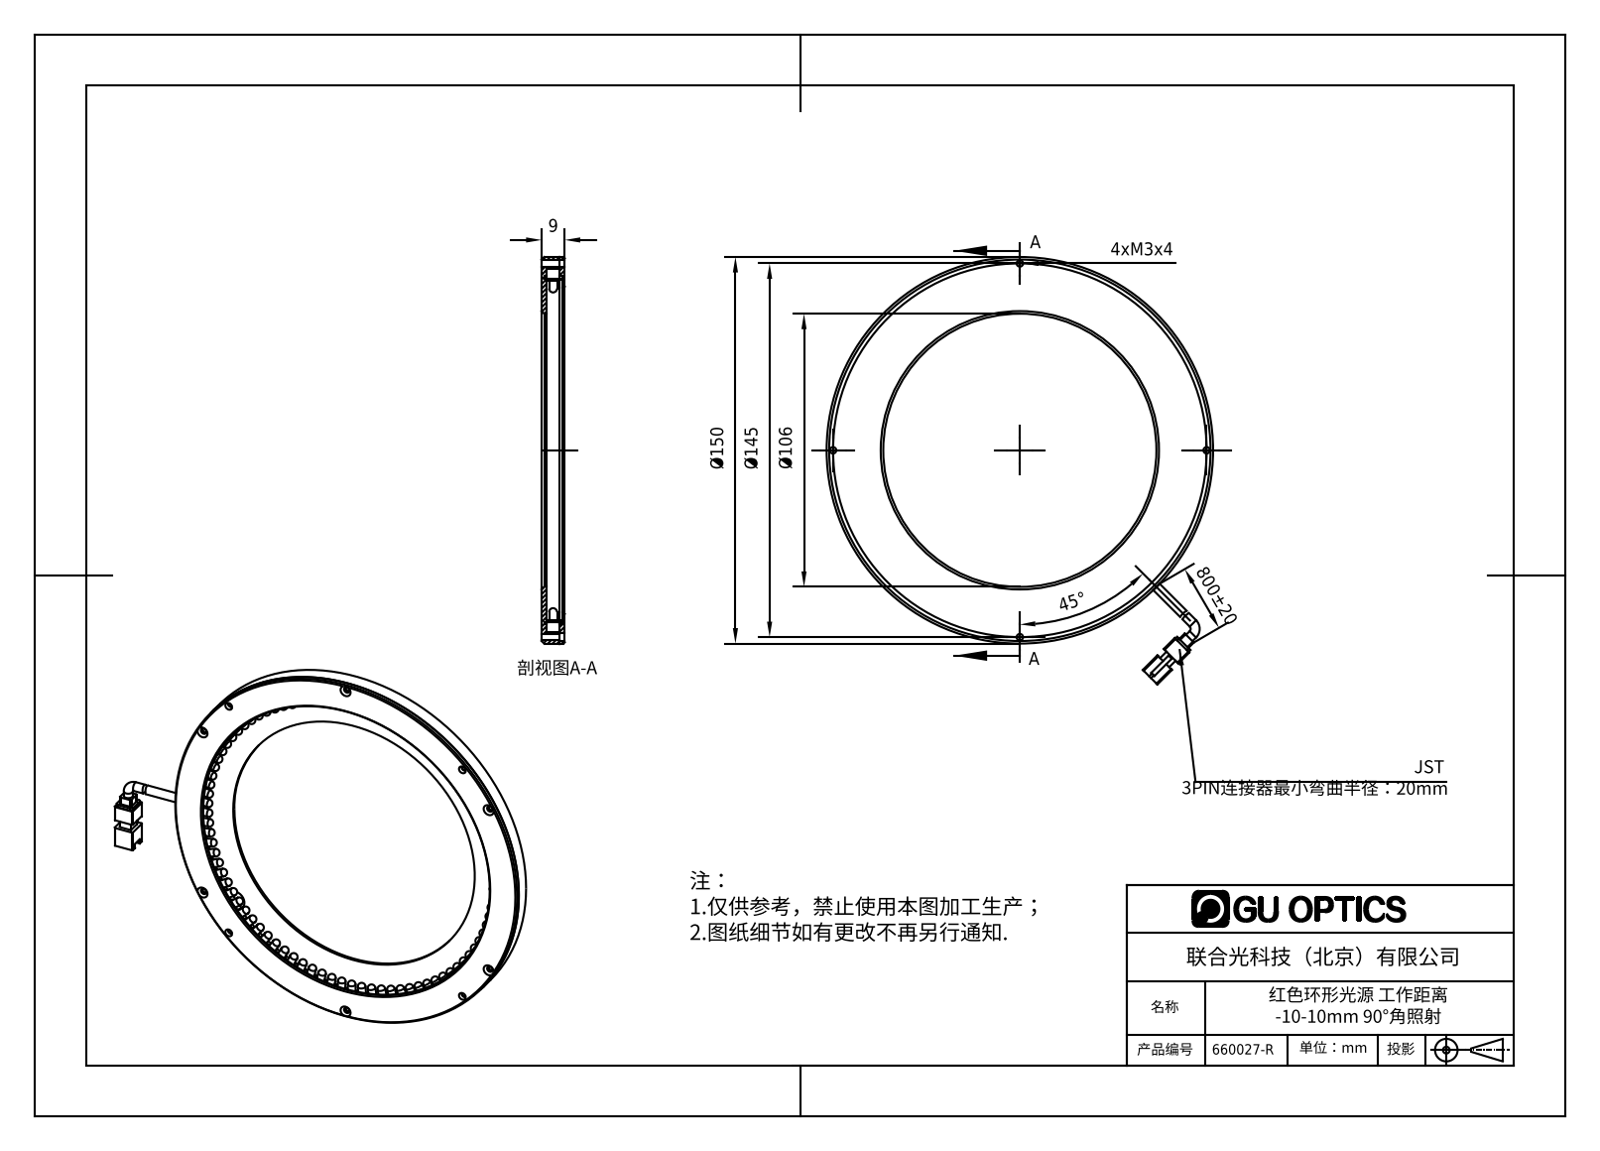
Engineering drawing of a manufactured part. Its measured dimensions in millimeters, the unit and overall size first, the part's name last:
Units: millimetres
Overall size (bounding box): 177 × 150 × 11
Round holes (diameter × count): ⌀1.6 ×6, ⌀2 ×6, ⌀2.4 ×6, ⌀2.5 ×4, ⌀3 ×4, ⌀8 ×2, ⌀3.5 ×1, ⌀106 ×1, ⌀126 ×1, ⌀132 ×1, ⌀135 ×1, ⌀141 ×1
Round bosses / shafts (diameter × count): ⌀4 ×90, ⌀3 ×90, ⌀3.5 ×2, ⌀150 ×1, ⌀134 ×1, ⌀133 ×1
Partial cylindrical surfaces — rounded edges, fillets, slot ends (radius × count): R0.5 ×8, R1 ×4, R2 ×2, R3.5 ×2
Main face-to-face distances: 2, 7, 5, 1, 9, 8, 6, 0.5, 1.5, 3.77
Hole centre spacings: 72.5, 72.49, 145, 88.27, 102.53, 115.03, 125.57, 133.96
Volume: 41 228 mm³ · Surface area: 51 986 mm²
Bodies: 95 solids, 1781 faces (1163 planar, 492 cylindrical, 126 other)
Part name (STEP PRODUCT): 660027-R
STEP written by: SolidWorks 2016 (AUTOMOTIVE_DESIGN)
